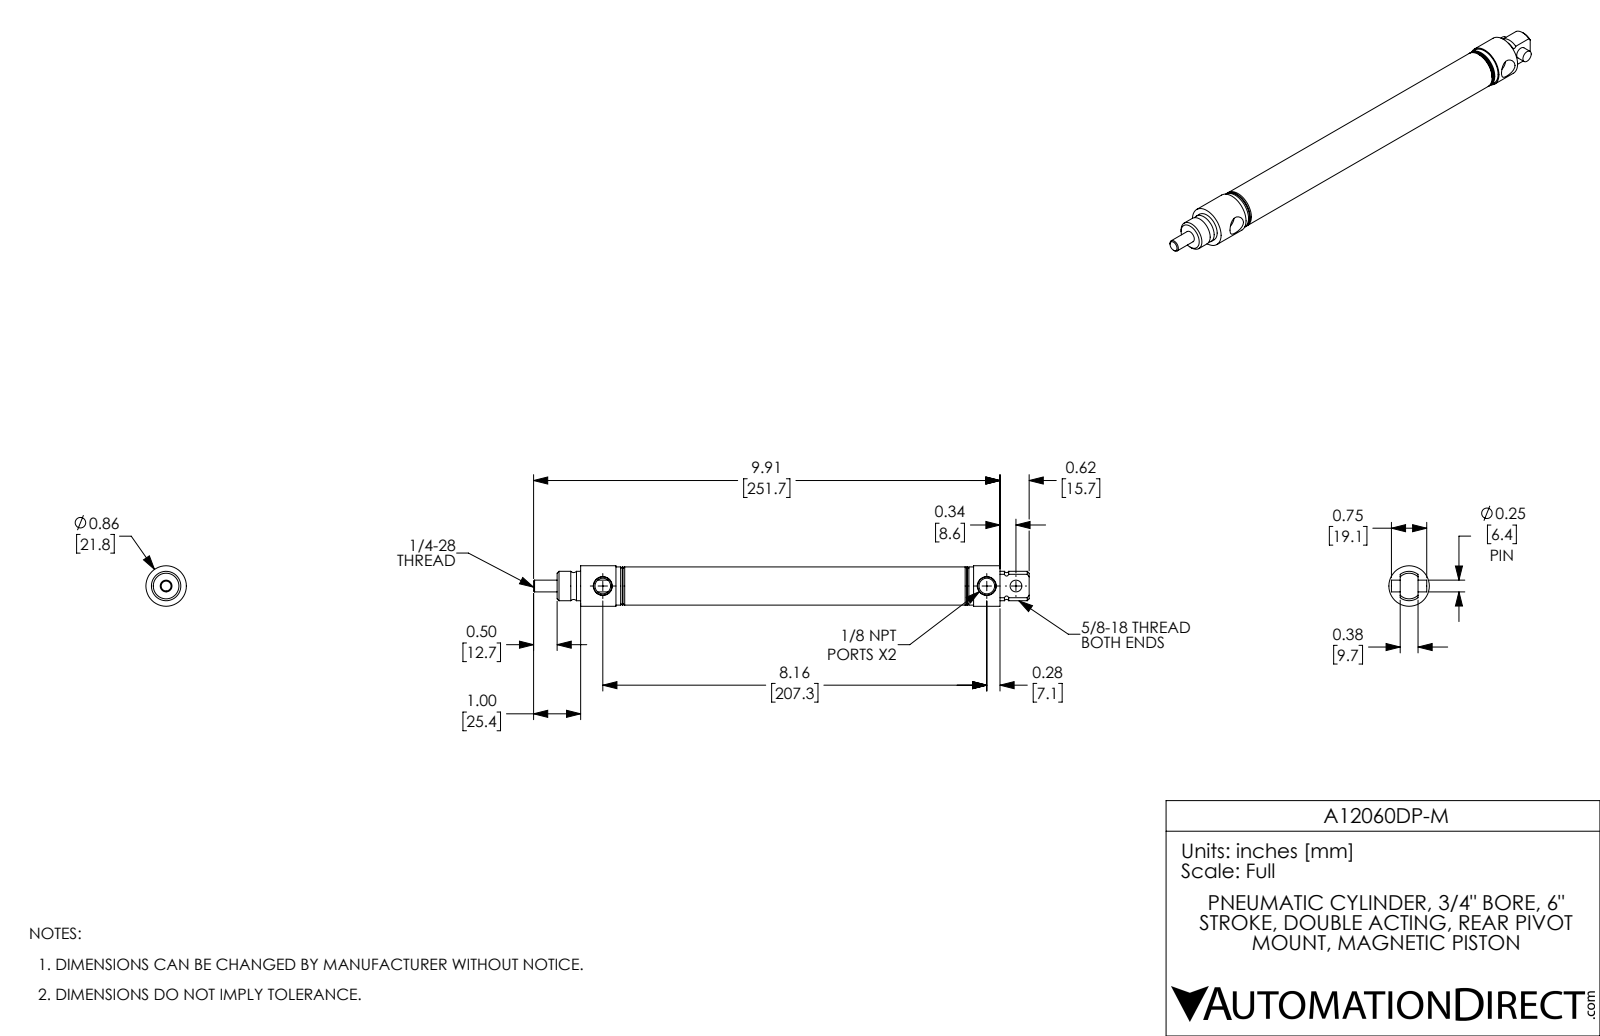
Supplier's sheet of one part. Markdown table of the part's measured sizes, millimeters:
| quantity | value |
| --- | --- |
| part name | A12060DP-M-PIN; A12060DP-M; A12060DP-M-MainBody; A12060DP-M-Rod |
| STEP written by | SolidWorks 2017 (AUTOMOTIVE_DESIGN) |
| units | millimeters |
| bodies | 3 solids, 91 faces (21 planar, 38 cylindrical, 32 other) |
| overall size | 267.5 × 21.8 × 21.8 |
| volume | 41 820 mm³ |
| surface area | 34 970 mm² |
| round holes (diameter × count) | 6.4 × 2, 8.4 × 2, 19.1 × 1 |
| round bosses / shafts (diameter × count) | 21.8 × 1, 20.6 × 1, 15.9 × 1 |
| main face-to-face distances | 12.7, 195.7, 165.1, 152.4, 30.6, 43.3, 195.7, 226.3, 183, 30.6 |
| hole center spacings | 15.7, 207.3, 223 |
